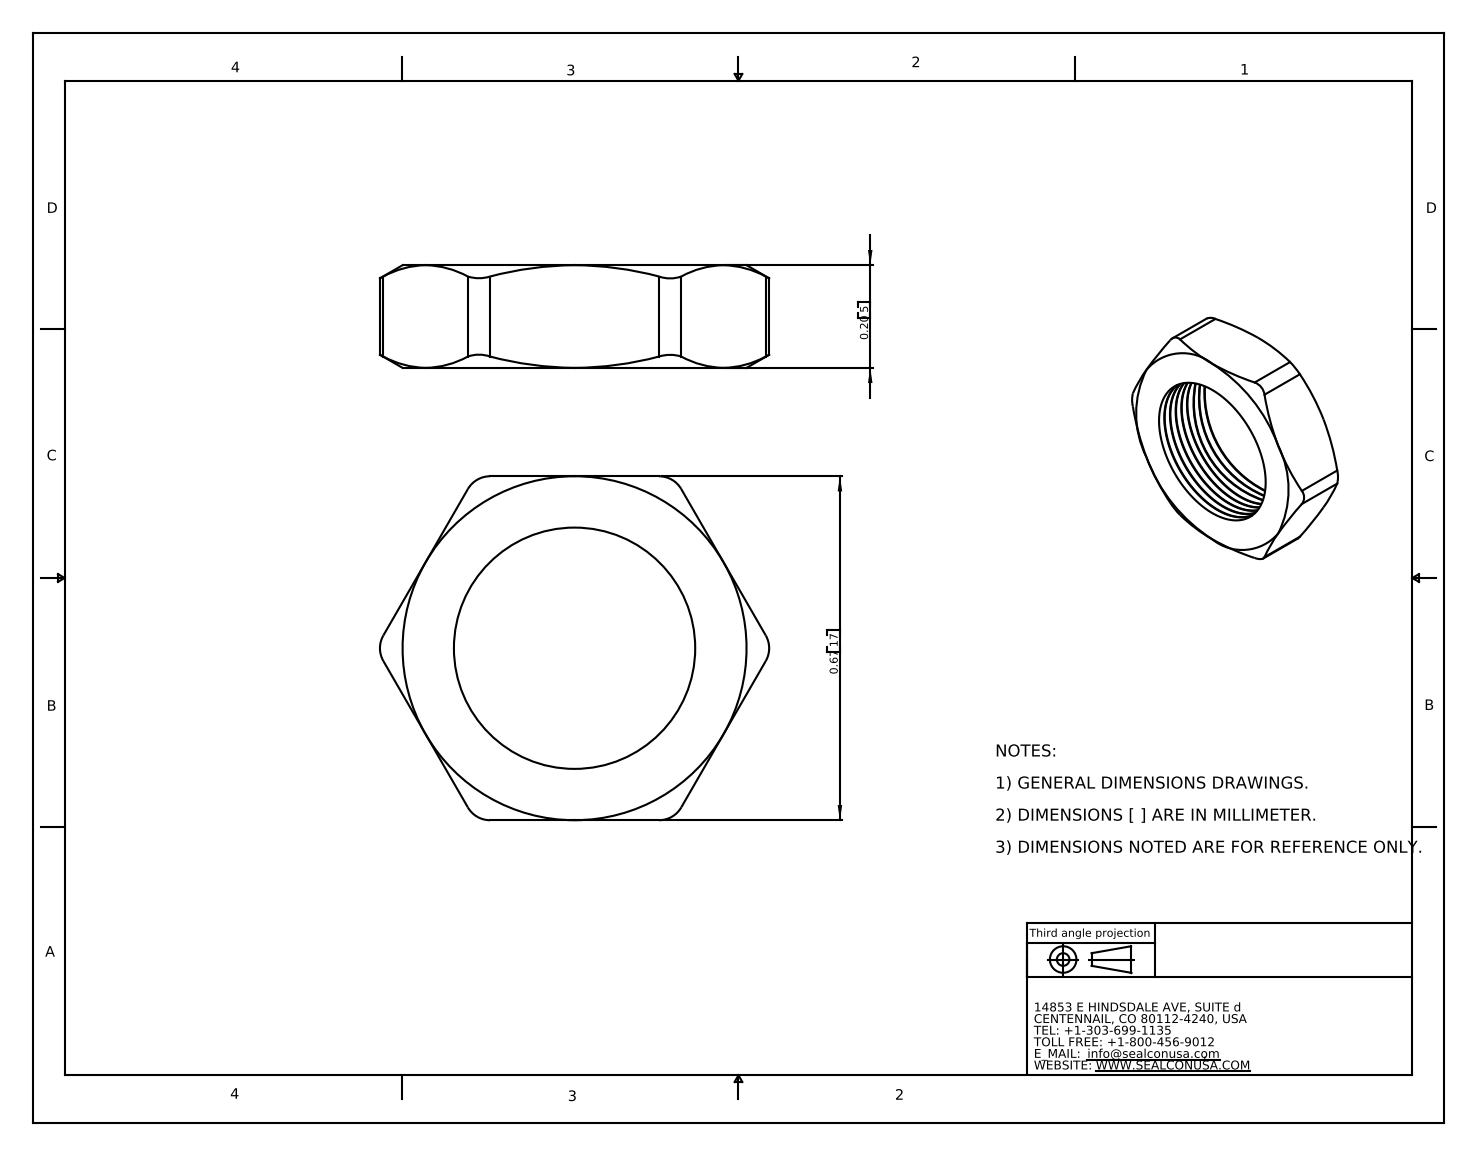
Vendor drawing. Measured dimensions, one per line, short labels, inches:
name: NM-12
written by: SolidWorks 2007 (CONFIG_CONTROL_DESIGN)
unit: in
bodies: 1 solid, 77 faces (8 planar, 23 cylindrical, 46 other)
size: 0.758 × 0.67 × 0.2
volume: 0.039 in³; area: 1.444 in²
holes: 1× ⌀0.47
rounds: 6× R0.05
face distances: 0.67, 0.2
